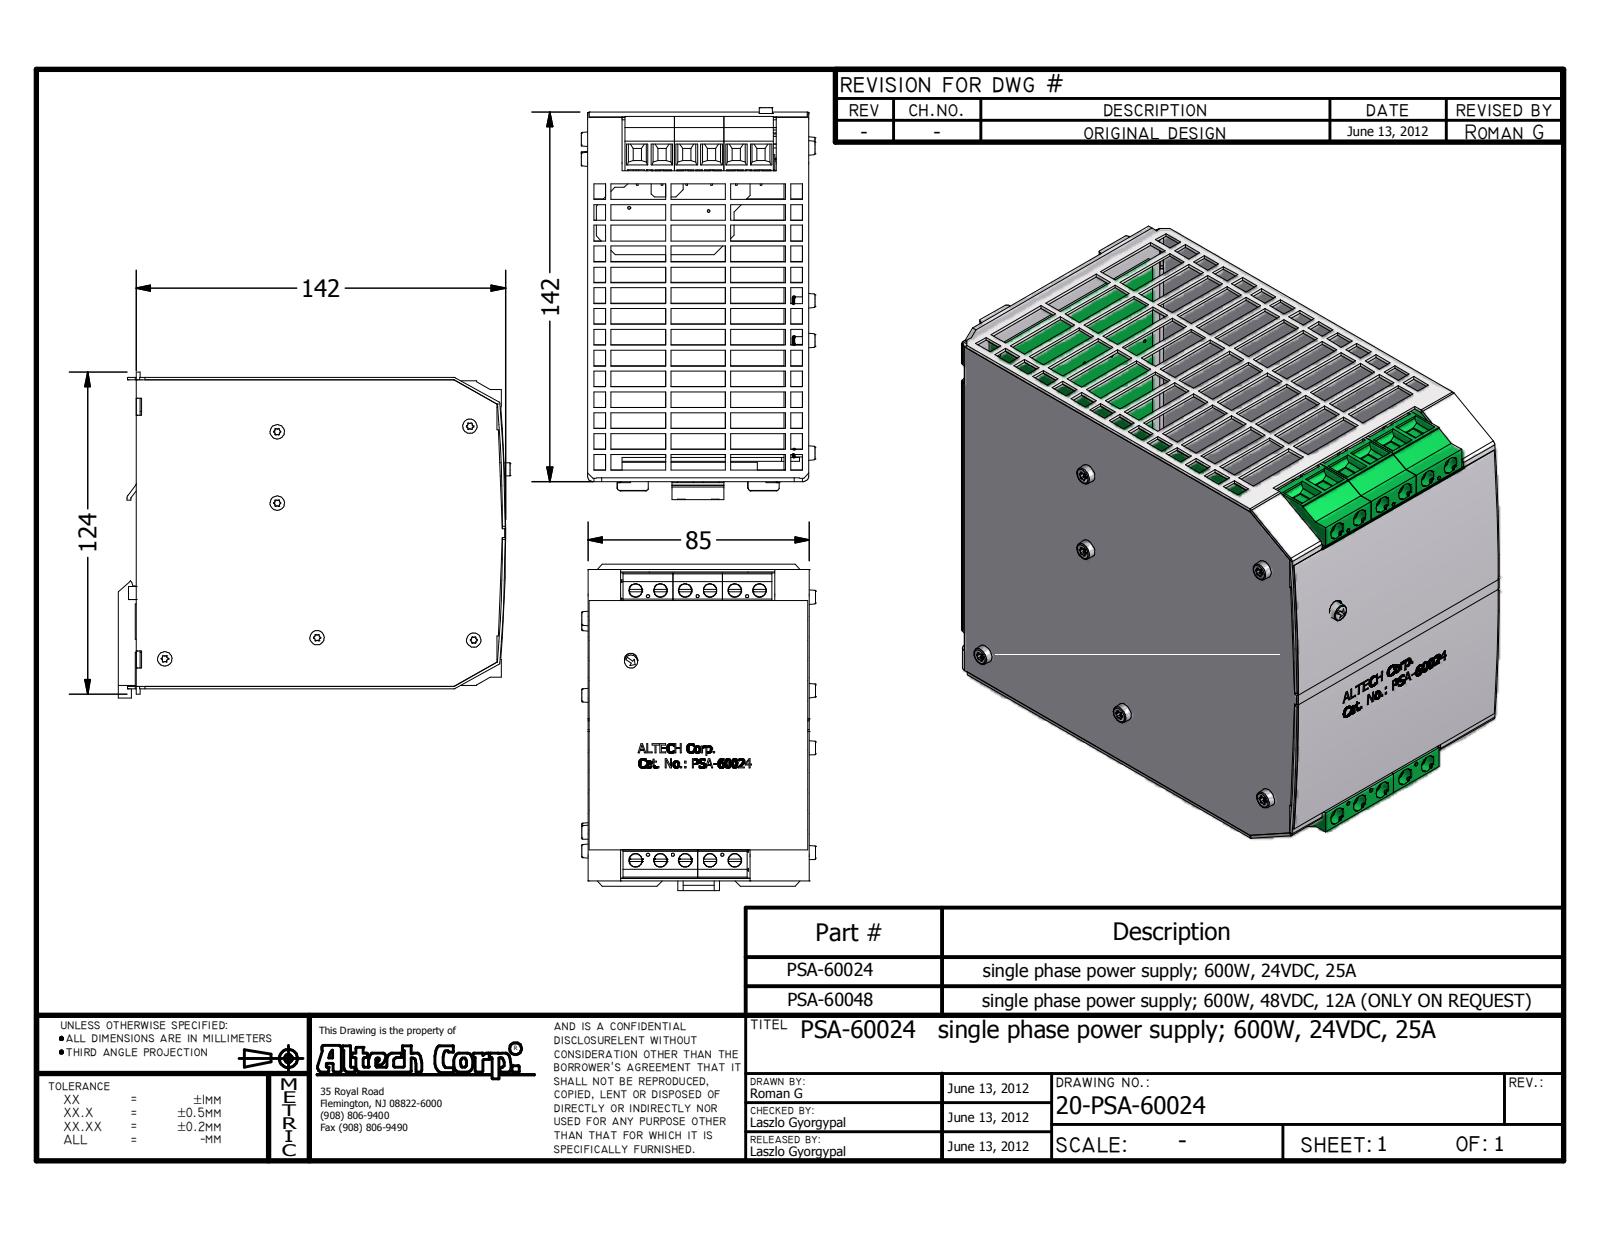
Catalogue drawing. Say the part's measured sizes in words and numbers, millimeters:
The part is named "ALTECH-PSA-60024". Its 3-D file was written by "Autodesk Inventor 2013 (CONFIG_CONTROL_DESIGN)". It is 3 solids with 3250 faces: 2389 planar, 549 cylindrical and 312 other. Overall it measures 150.5 by 125.2 by 89.8 millimeters. Its volume is 173 700 cubic millimeters and its surface area 209 700 square millimeters. Round holes: 80 of diameter 1, 11 of diameter 5.2, 8 of diameter 2.3, 7 of diameter 3.3, 6 of diameter 1.2, 4 of diameter 0.9, 4 of diameter 2.8, 4 of diameter 3.1, 2 of diameter 2, 2 of diameter 2.2, 2 of diameter 3.5. Round bosses or shafts: 12 of diameter 5, 11 of diameter 1.3, 10 of diameter 3, 7 of diameter 2.7, 2 of diameter 6.7, 2 of diameter 4.7, 2 of diameter 1.5, 1 of diameter 9. Partial cylindrical surfaces (rounded edges, fillets, slot ends): 61 of radius 0.3, 60 of radius 0.6, 44 of radius 0.1, 17 of radius 0.2, 16 of radius 0.6, 14 of radius 1.2, 10 of radius 1, 8 of radius 0.5. The main face-to-face distances are 1.5, 83.5, 1.6, 85, 82, 7.9, 6.4, 75.6, 77.1, 9.5. The hole center spacings are 5.2, 100.7, 9.5, 19.1, 102.4, 14.5, 101.5, 104.1.
